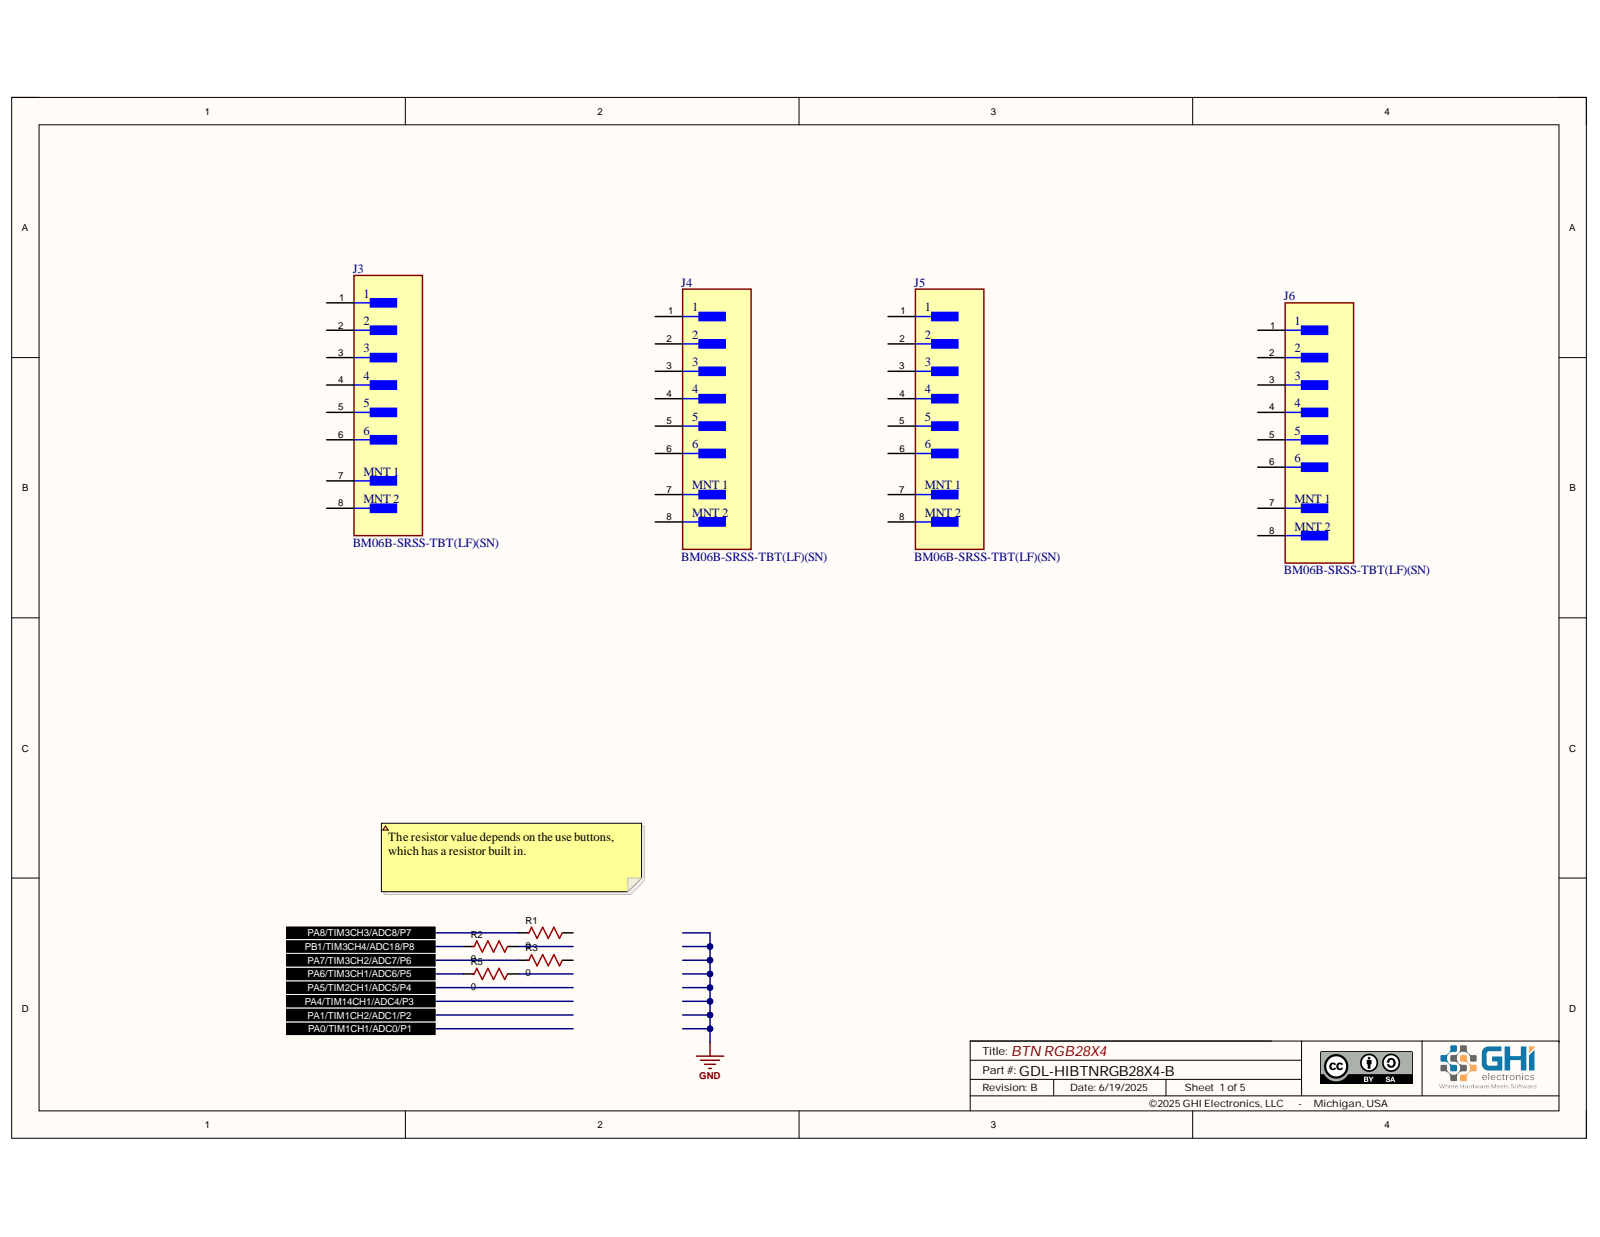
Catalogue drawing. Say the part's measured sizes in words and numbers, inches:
The part is named "PCB; Board; J6; Conn_JST_BM06B-SRSS-TBT_LF_SN_eec (+6 more)". Its 3-D file was written by "Open CASCADE 7.5 (AUTOMOTIVE_DESIGN)". It is 180 solids with 3735 faces: 1920 planar, 1064 cylindrical and 751 other. Overall it measures 3.622 by 3.622 by 1.496 inches. Its volume is 2.883 cubic inches and its surface area 81.69 square inches. Round holes: 4 of diameter 0.118, 4 of diameter 0.748, 4 of diameter 0.906, 4 of diameter 0.945, 4 of diameter 1.142, 2 of diameter 0.04. Round bosses or shafts: 4 of diameter 1.26, 4 of diameter 1.102, 4 of diameter 0.827, 4 of diameter 0.787. Partial cylindrical surfaces (rounded edges, fillets, slot ends): 35 of radius 0.005, 24 of radius 0.039, 14 of radius 0.006, 4 of radius 0.004, 4 of radius 0.138, 2 of radius 0.007, 2 of radius 0.007, 2 of radius 0.007. The main face-to-face distances are 0.063, 0.079, 0.63, 0.118, 0.315, 0.512, 0.02, 0.472, 0.3, 0.363. The hole center spacings are 1.811, 2.691, 1.086, 2.561, 3.346, 3.647, 1.809, 2.558.
